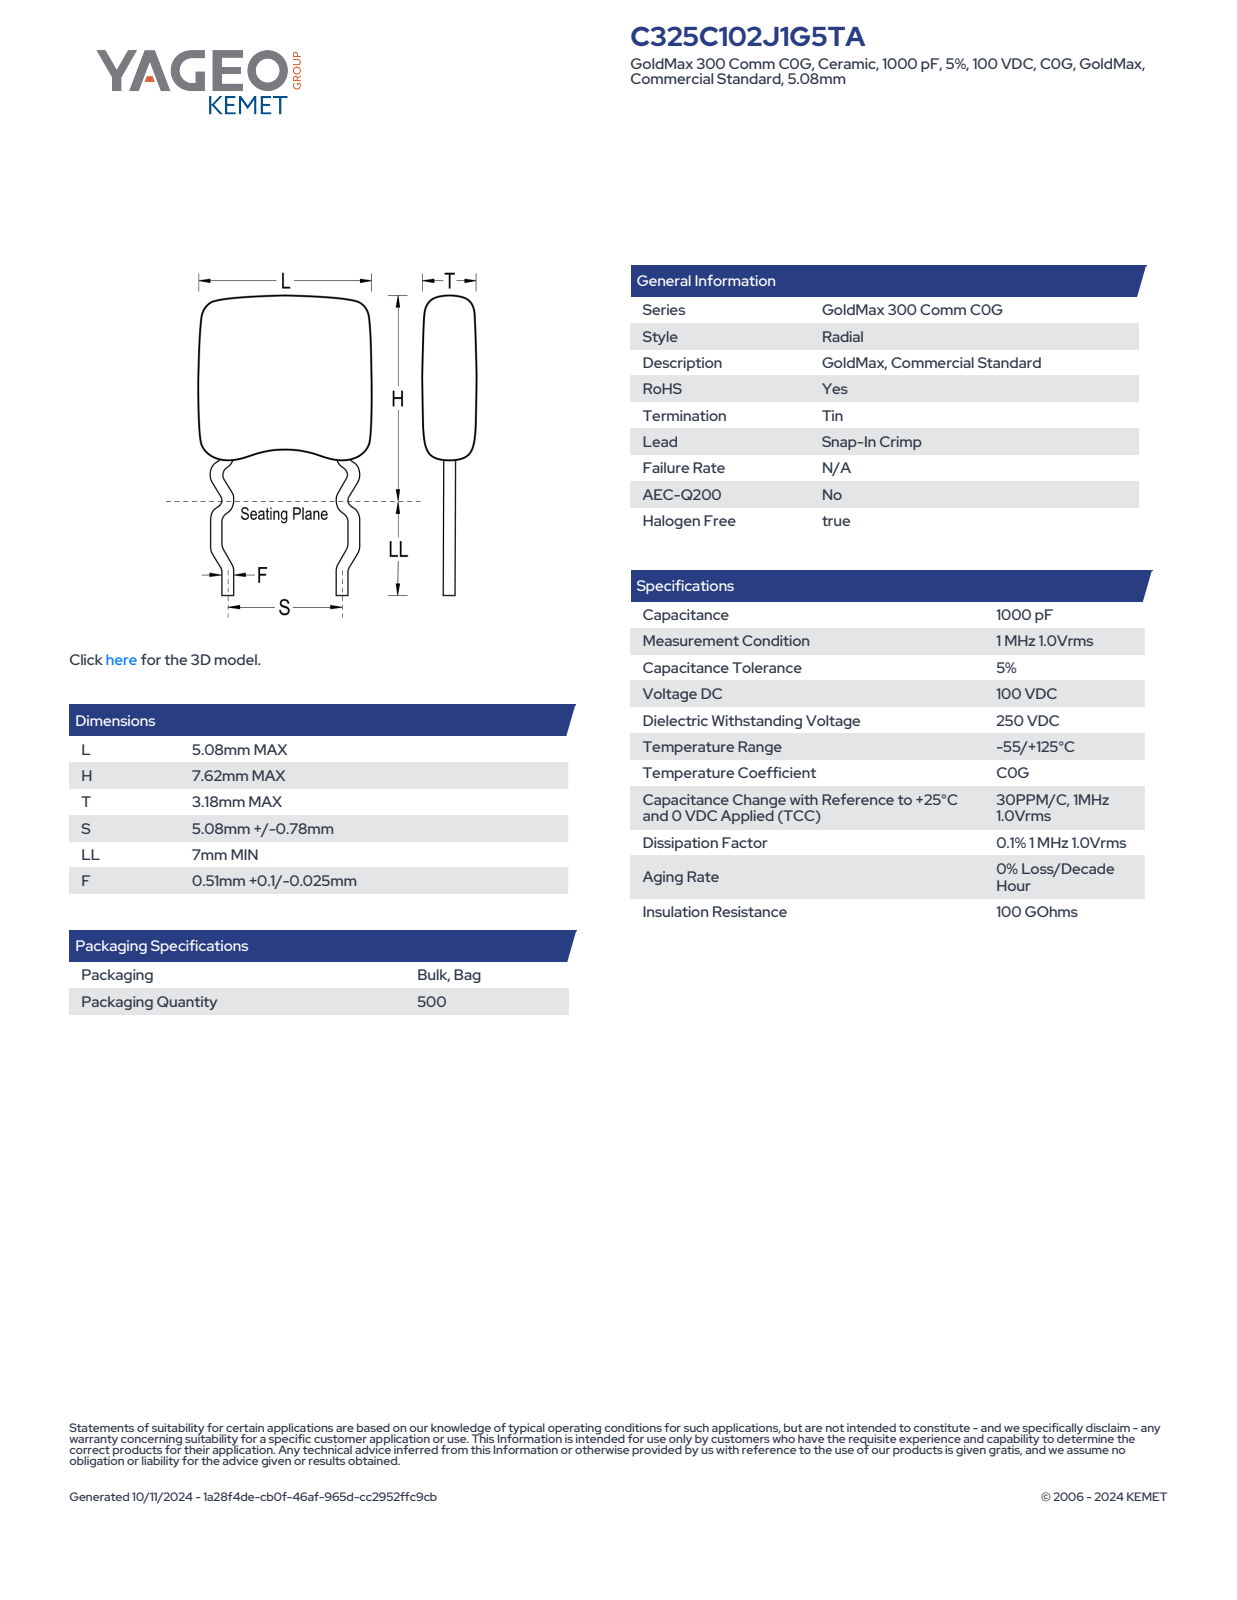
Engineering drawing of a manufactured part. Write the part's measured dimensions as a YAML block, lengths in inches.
part_name: "CCR_SICR_5.08X7.62_L5.08H7.62T3.18S5.08LL7F0.51"
step_written_by: "SolidWorks 2014 (AUTOMOTIVE_DESIGN)"
units: inches
bodies: {solids: 4, faces: 157, planar: 68, cylindrical: 46, other: 43}
overall_size: [0.59, 0.281, 0.126]
volume: 0.004
surface_area: 0.198
round_bosses_or_shafts:
  - {diameter: 0.02, count: 18}
partial_cylinders:
  - {radius: 0.039, count: 10}
face_to_face_distances: [0.125, 0.2, 0.189, 0.126, 0.4, 0.59, 0.084, 0.106, 0.506, 0.484]
